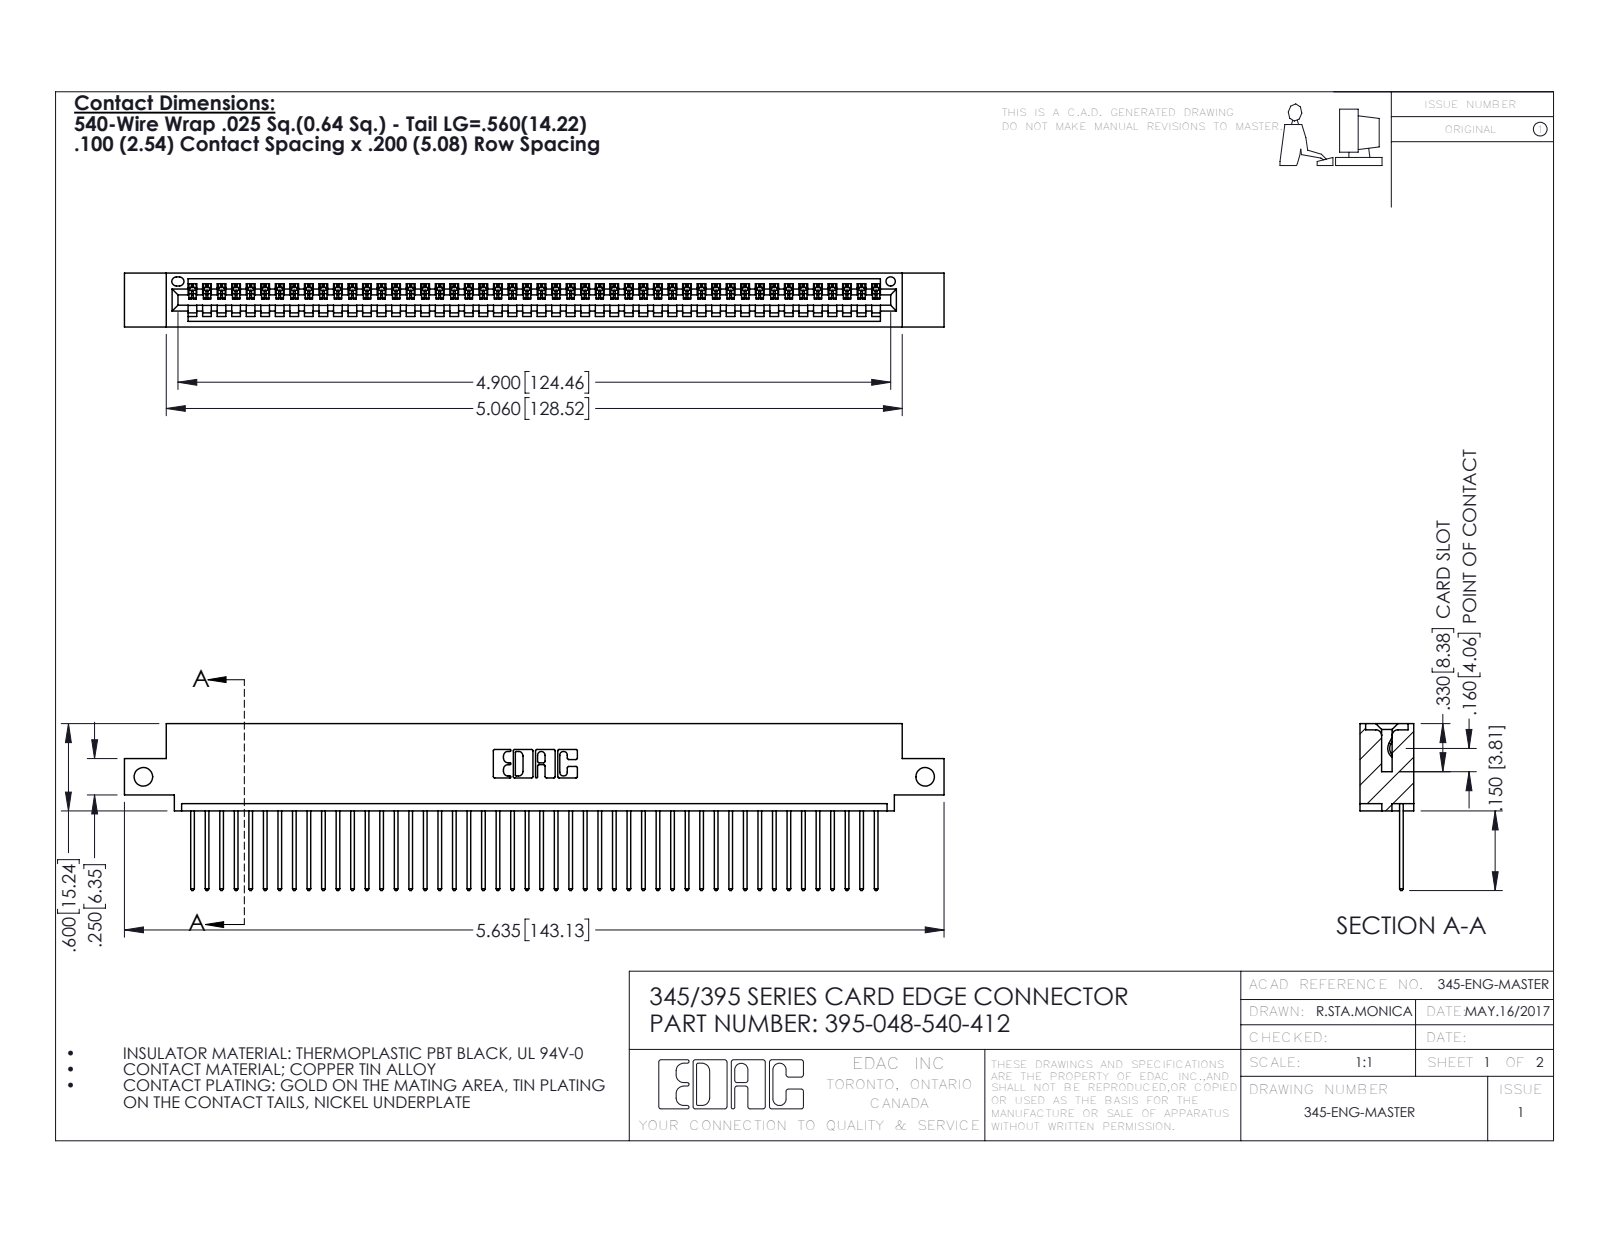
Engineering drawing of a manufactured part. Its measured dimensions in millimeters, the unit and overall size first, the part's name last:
Units: millimetres
Overall size (bounding box): 143.1 × 29.1 × 9.4
Round holes (diameter × count): ⌀3.3 ×2, ⌀1.6 ×1
Partial cylindrical surfaces — rounded edges, fillets, slot ends (radius × count): R0.2 ×96, R0.3 ×96, R0.3 ×22, R0.2 ×6, R0.8 ×6, R0.7 ×3, R0.8 ×2, R1 ×2
Main face-to-face distances: 7.6, 1.8, 9.4, 2.5, 6.9, 0.6, 5.1, 5.7, 3.8, 1.8
Hole centre spacings: 136.5
Volume: 13 600 mm³ · Surface area: 18 490 mm²
Bodies: 49 solids, 2914 faces (2004 planar, 910 cylindrical, 0 other)
Part name (STEP PRODUCT): 395-048-540-412; 345-292-001_345-293-140; 345 Part_0.110 Offset - Side Mount
STEP written by: SolidWorks 2016 (CONFIG_CONTROL_DESIGN)
